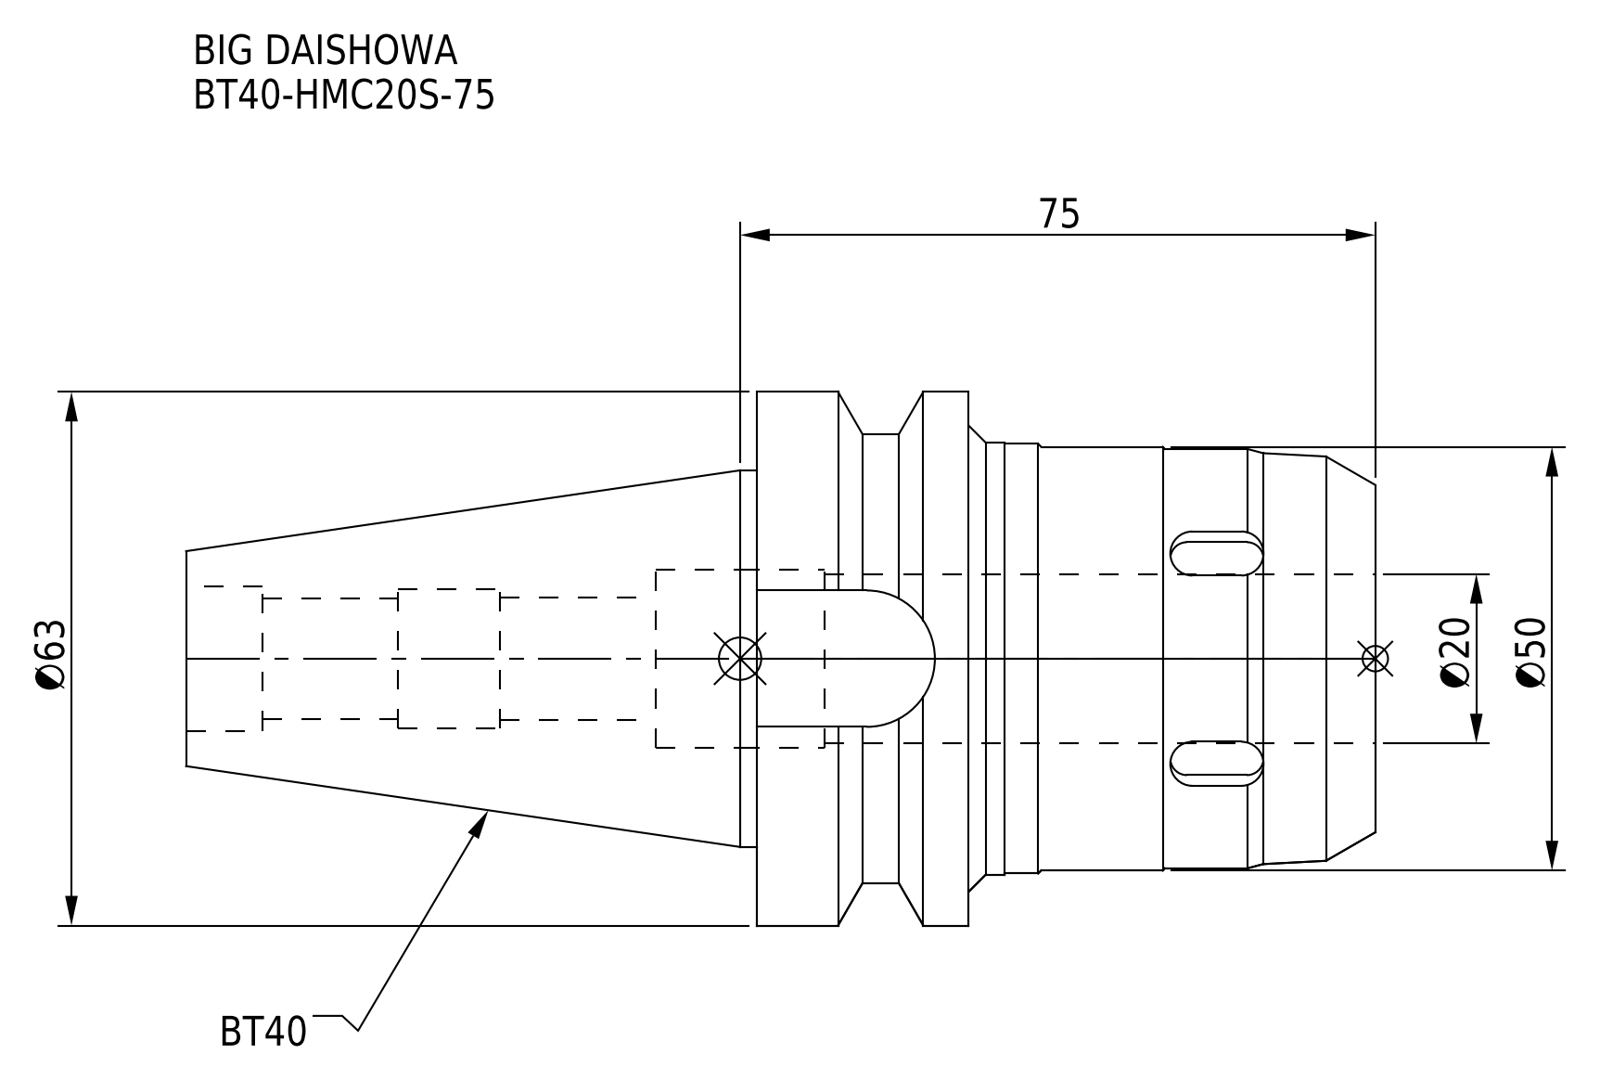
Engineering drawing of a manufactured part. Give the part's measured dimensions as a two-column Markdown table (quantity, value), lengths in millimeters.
| quantity | value |
| --- | --- |
| part name | BT40-HMC20S-75 |
| STEP written by | CREO PARAMETRIC BY PTC INC, 2016380 (AUTOMOTIVE_DESIGN) |
| units | millimeters |
| bodies | 1 solid, 98 faces (34 planar, 42 cylindrical, 22 other) |
| overall size | 140.4 × 63 × 63 |
| volume | 187 121 mm³ |
| surface area | 33 666 mm² |
| round holes (diameter × count) | 14.2 × 1, 14.5 × 1, 16.5 × 1, 17 × 1, 20 × 1, 21 × 1 |
| round bosses / shafts (diameter × count) | 63 × 1, 53 × 1, 51 × 1, 50.7 × 1, 50 × 1, 49.5 × 1, 44.45 × 1 |
| partial cylindrical surfaces (radius × count) | 3 × 6, 8.05 × 1 |
| main face-to-face distances | 73, 25, 48, 45, 67.4, 140.4, 92.4, 37, 55.4, 12 |
